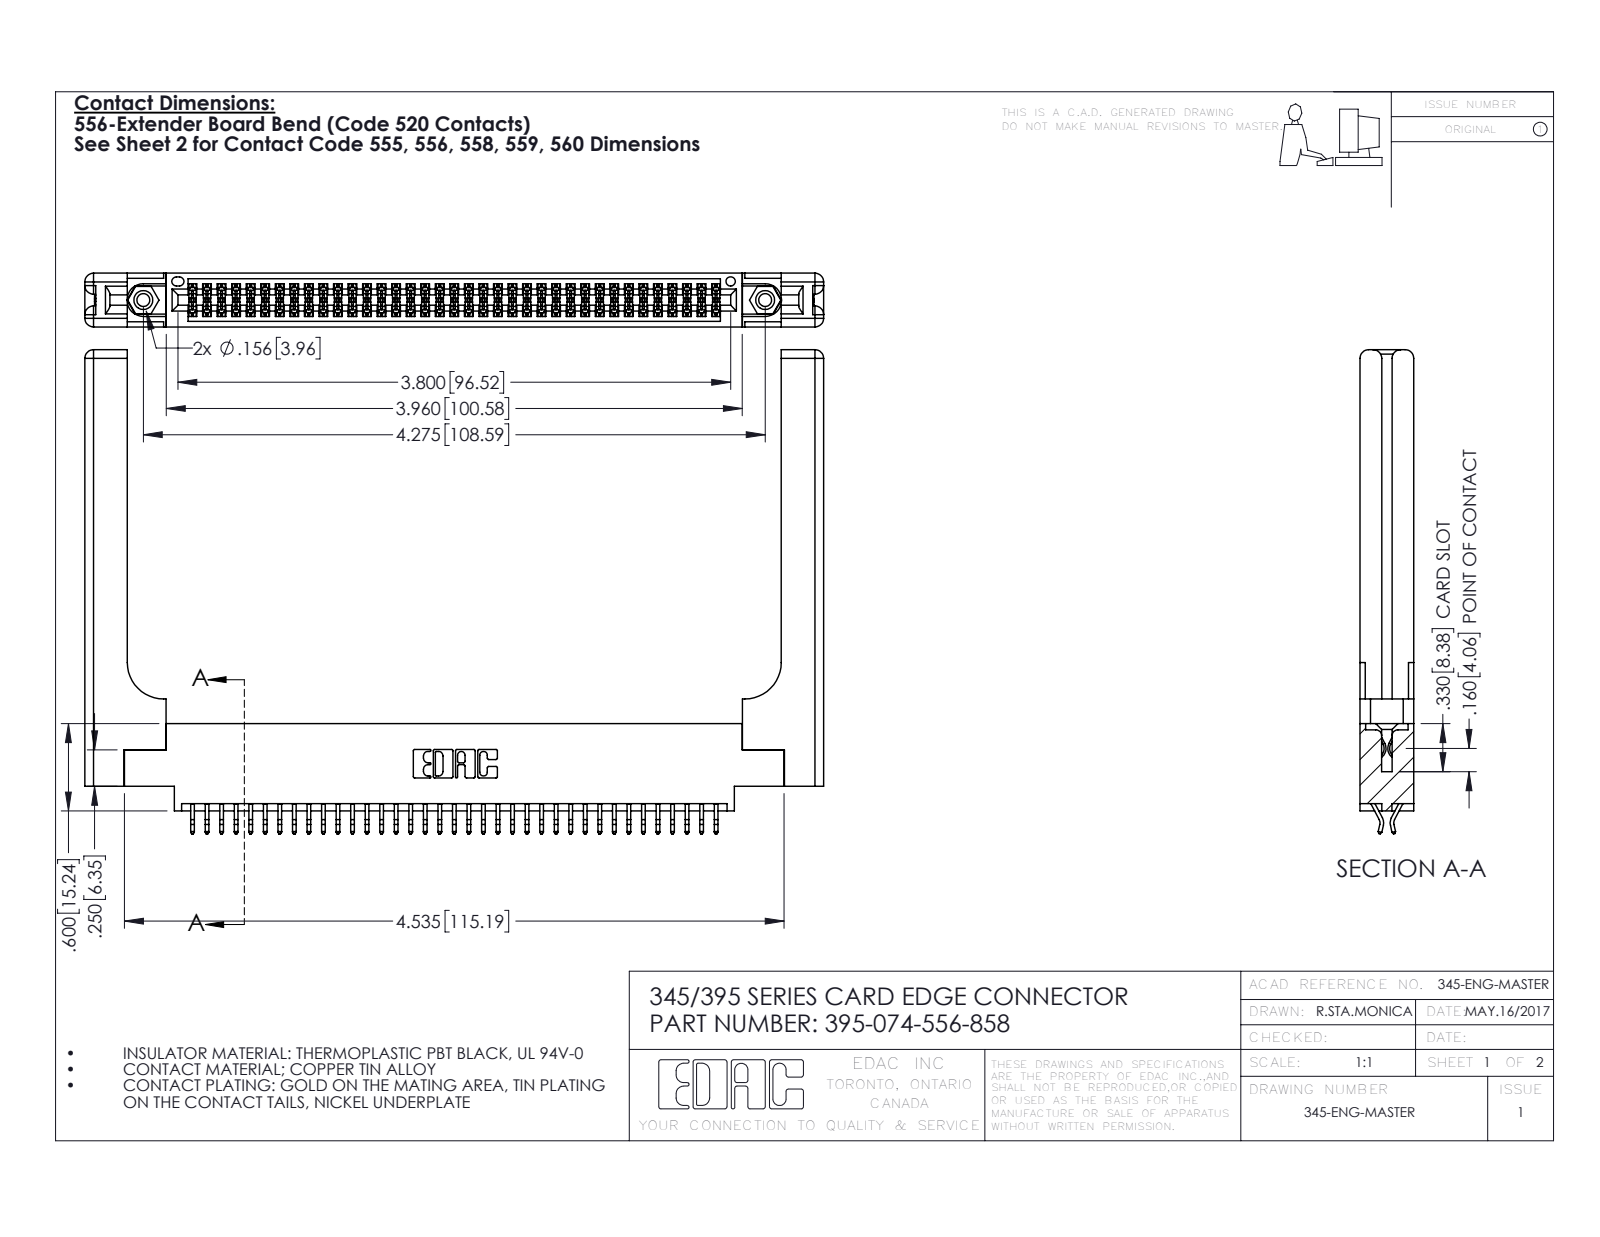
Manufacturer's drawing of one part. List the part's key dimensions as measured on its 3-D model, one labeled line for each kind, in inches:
Part name (STEP PRODUCT): 345 Part_0.170 Offset - 0.156 Dia-TH; 345-220-058_345-220-058; 345-250-001_345-250-001-102; 395-074-556-858 (+1 more)
STEP written by: SolidWorks 2016 (CONFIG_CONTROL_DESIGN)
Units: inches
Bodies: 79 solids, 4530 faces (2970 planar, 1500 cylindrical, 60 other)
Overall size (bounding box): 5.079 × 3.327 × 0.37
Volume: 1.272 in³ · Surface area: 36.15 in²
Round holes (diameter × count): ⌀0.089 ×2, ⌀0.125 ×2, ⌀0.156 ×2, ⌀0.064 ×1
Round bosses / shafts (diameter × count): ⌀0.155 ×2
Partial cylindrical surfaces — rounded edges, fillets, slot ends (radius × count): R0.006 ×111, R0.01 ×22, R0.06 ×16, R0.007 ×6, R0.031 ×6, R0.026 ×3, R0.01 ×2, R0.014 ×2
Main face-to-face distances: 0.37, 0.072, 0.298, 0.025, 0.098, 0.272, 0.2, 0.225, 0.148, 0.15
Hole centre spacings: 0.27, 4.039, 4.275
